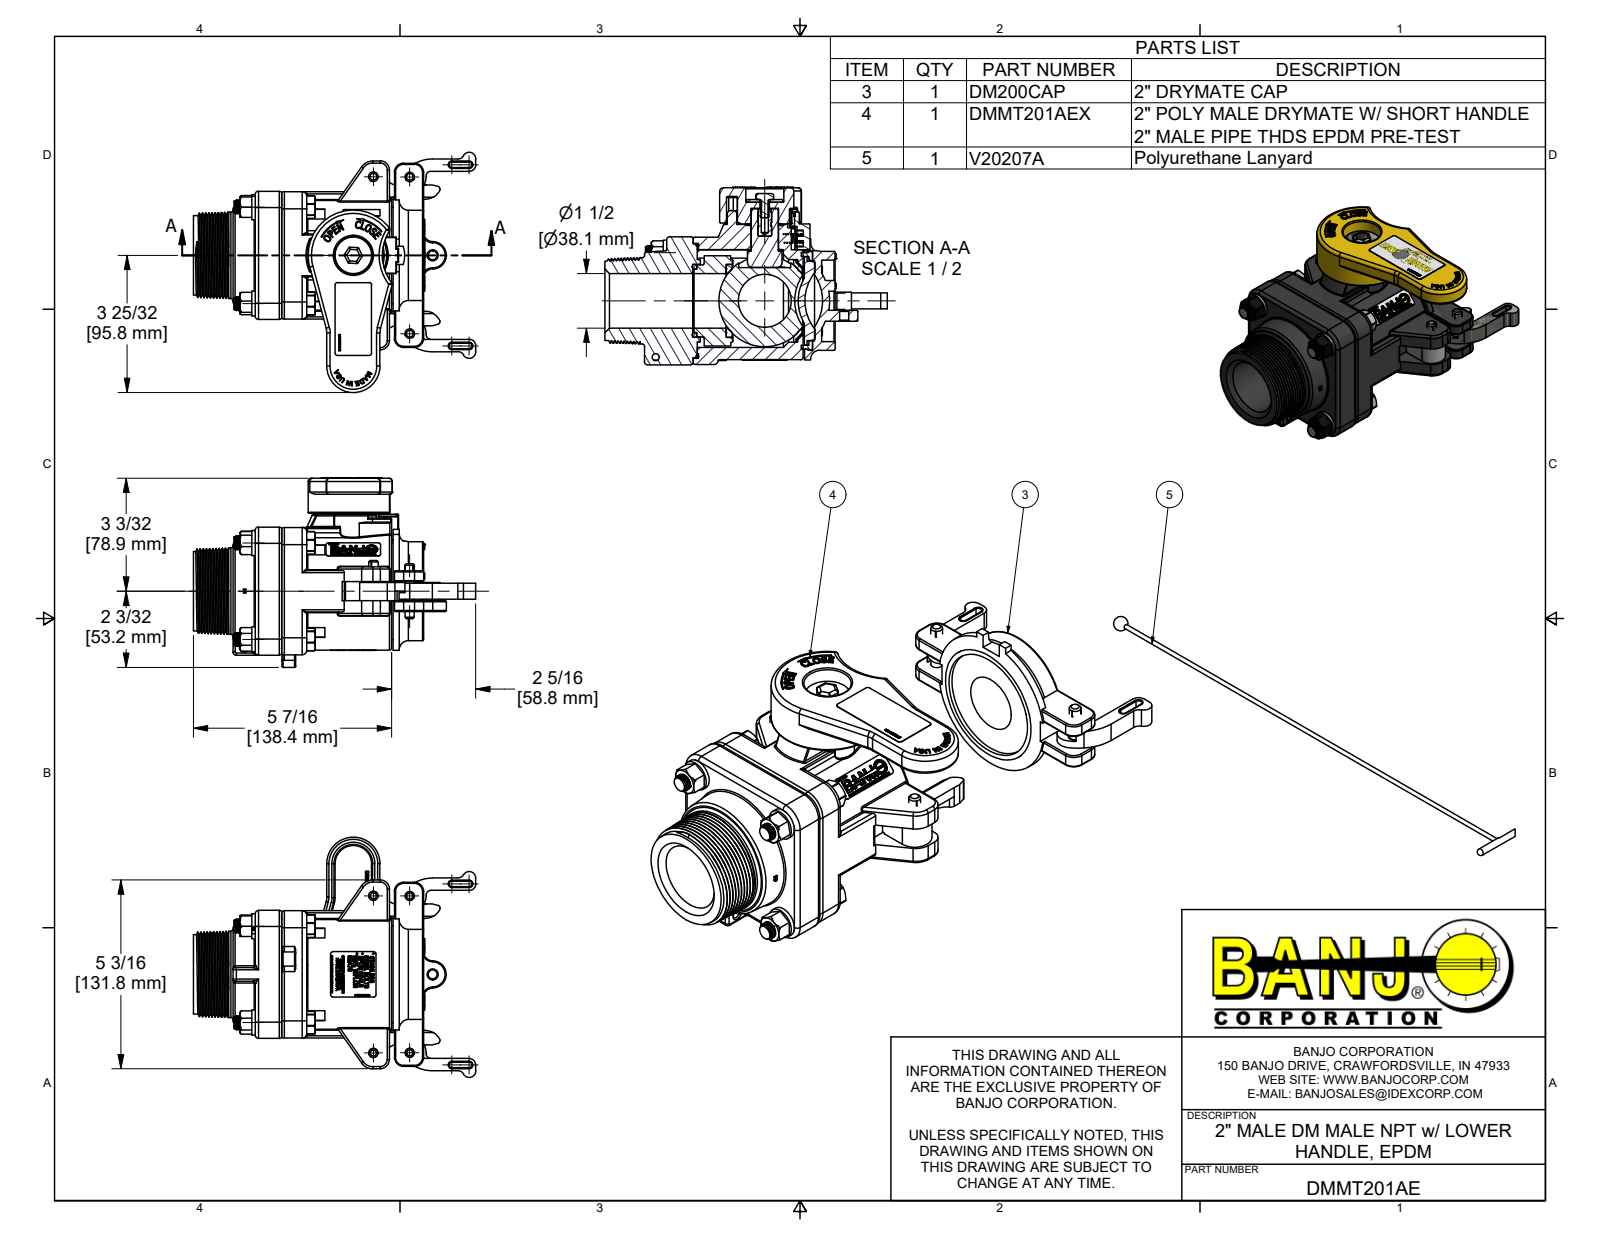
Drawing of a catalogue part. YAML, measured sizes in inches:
part_name: "DMMT201AE; DMMT201AEX; DM20254; DM20254MY (+8 more)"
step_written_by: "Autodesk Inventor 2022 (AUTOMOTIVE_DESIGN)"
units: inches
bodies: {solids: 45, faces: 6002, planar: 2808, cylindrical: 902, other: 2292}
overall_size: [7.764, 6.6, 5.217]
volume: 48.04
surface_area: 393.6
round_holes:
  - {diameter: 0.25, count: 5}
  - {diameter: 0.375, count: 5}
  - {diameter: 0.256, count: 4}
  - {diameter: 0.307, count: 4}
  - {diameter: 0.385, count: 4}
  - {diameter: 0.406, count: 4}
  - {diameter: 0.42, count: 4}
  - {diameter: 0.125, count: 3}
  - {diameter: 0.2, count: 2}
  - {diameter: 0.196, count: 1}
  - {diameter: 0.227, count: 1}
  - {diameter: 0.26, count: 1}
round_bosses_or_shafts:
  - {diameter: 0.324, count: 60}
  - {diameter: 0.687, count: 4}
  - {diameter: 0.375, count: 4}
  - {diameter: 0.26, count: 4}
  - {diameter: 0.249, count: 4}
  - {diameter: 0.28, count: 3}
  - {diameter: 2.48, count: 2}
  - {diameter: 3.25, count: 1}
partial_cylinders:
  - {radius: 0.03, count: 107}
  - {radius: 0.06, count: 53}
  - {radius: 0.02, count: 20}
  - {radius: 0.09, count: 19}
  - {radius: 0.01, count: 12}
  - {radius: 0.125, count: 10}
  - {radius: 0.162, count: 8}
  - {radius: 0.25, count: 8}
face_to_face_distances: [0.298, 2.91, 3.17, 3.75, 0.84, 0.035, 0.297, 3.51, 0.822, 3.28]
hole_center_spacings: [2.653, 1.872, 1.88, 2.648, 2.658, 3.752, 0.95, 0.986]
